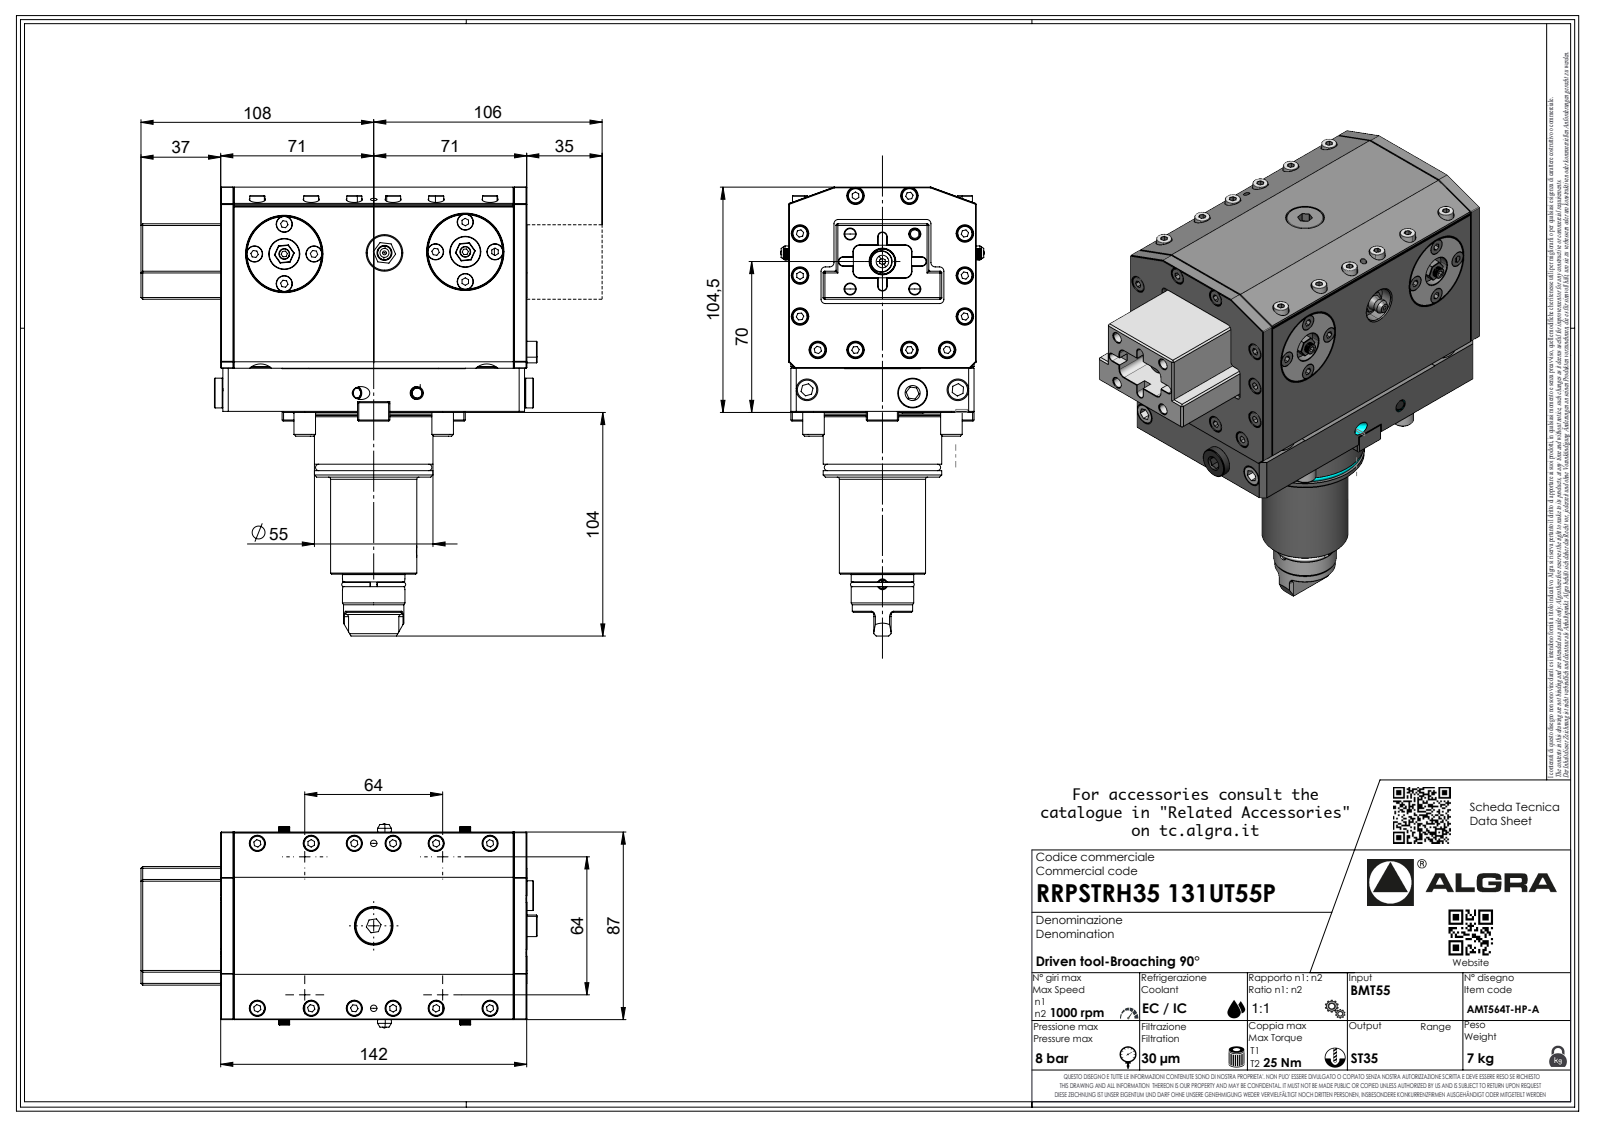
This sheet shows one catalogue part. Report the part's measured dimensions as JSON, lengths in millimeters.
{"part_name": "RRPSTRH35131UT55P", "step_written_by": "SolidWorks 2023 (AUTOMOTIVE_DESIGN)", "units": "millimeters", "bodies": {"solids": 0, "faces": 1572, "planar": 862, "cylindrical": 279, "other": 431}, "overall_size": [208.2, 183.82, 94.6], "round_holes": [[4.5, 12], [7.5, 12], [8.1, 2], [15, 2], [35.5, 2], [1.05, 1], [5, 1], [10.2, 1], [12, 1], [47.3, 1]], "round_bosses_or_shafts": [[7, 14], [12, 3], [35, 2], [10, 2], [5, 2], [55, 1], [54.6, 1], [50.2, 1]], "partial_cylinders_radius": [[2.5, 13], [2, 12], [0.2, 8], [0.5, 8], [3.6, 8], [0.17, 7], [0.26, 7], [1.85, 7]], "face_to_face_distances": [87, 1, 142, 86, 104, 6, 20, 84, 0.5, 20.3], "hole_center_spacings": [76.5, 12.54, 17.5, 17.56, 19, 19.5, 25, 30.02]}
